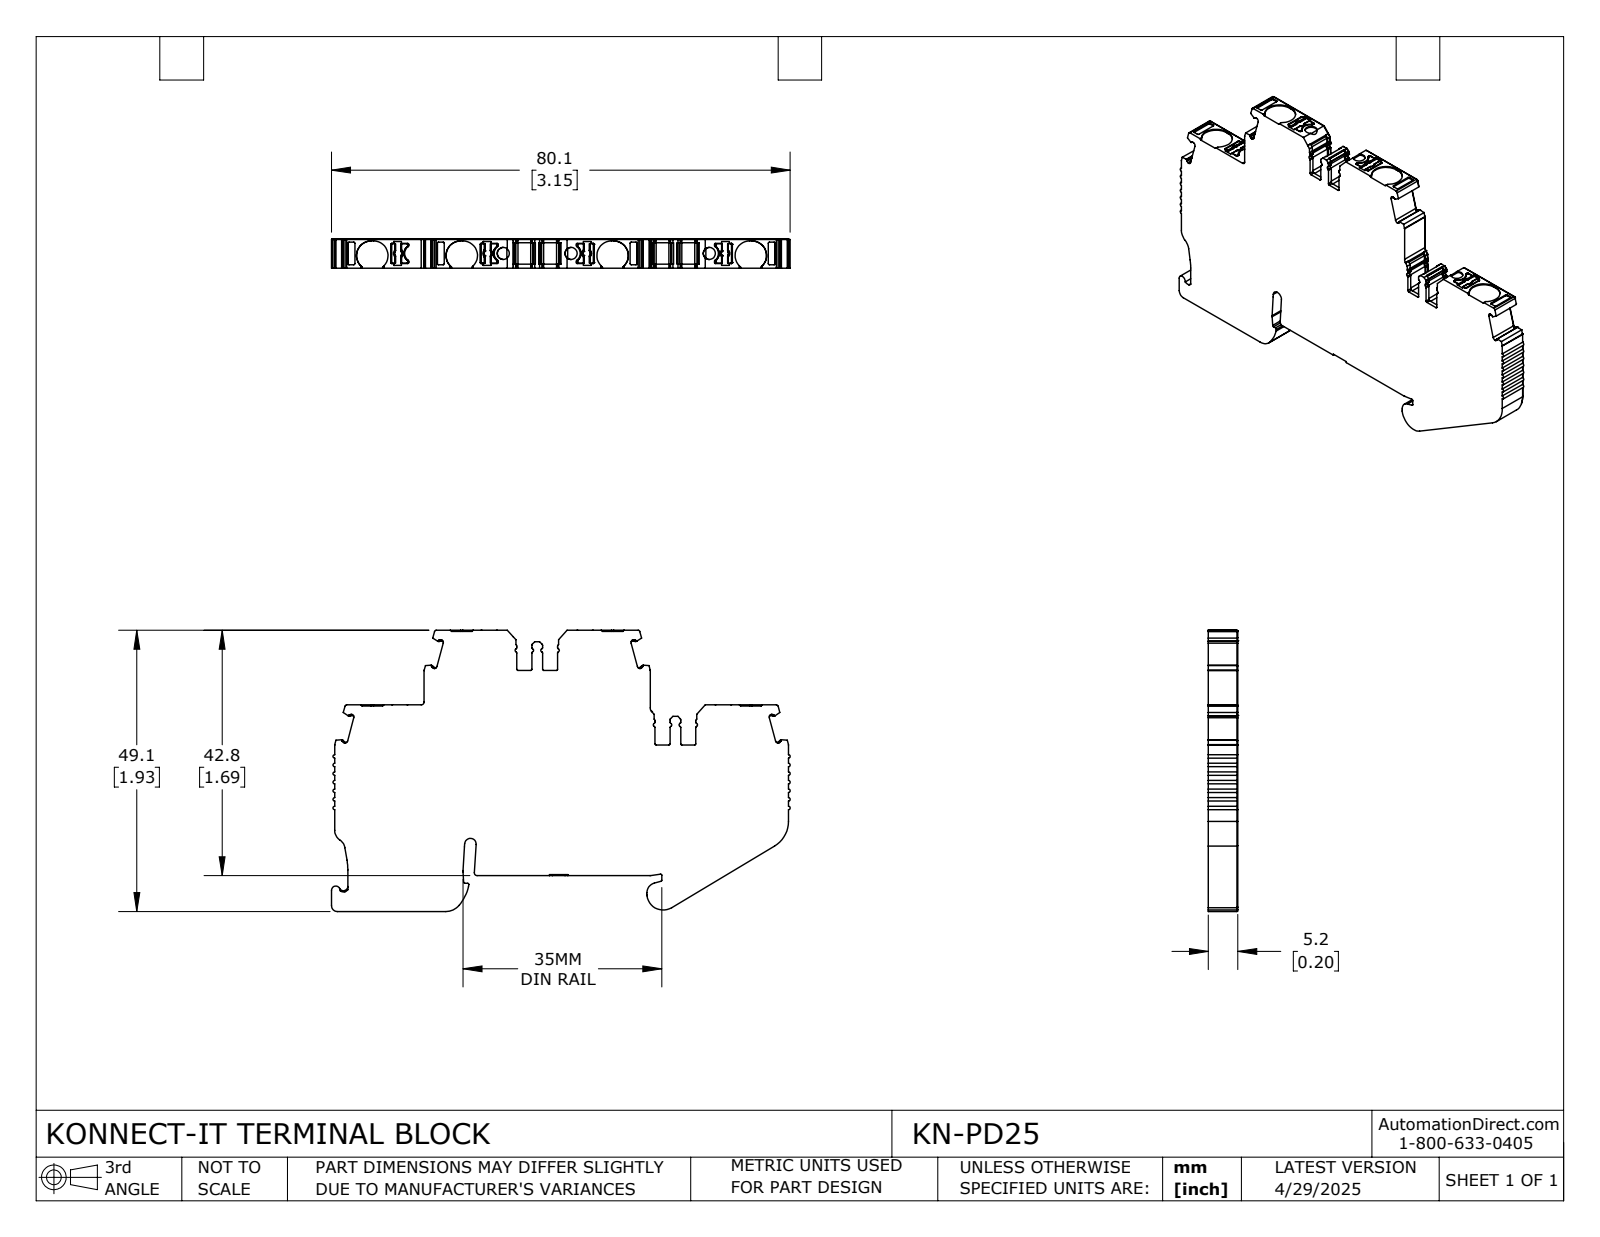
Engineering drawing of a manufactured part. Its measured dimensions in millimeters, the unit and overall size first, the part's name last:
Units: millimetres
Overall size (bounding box): 80.1 × 49.1 × 5.2
Round holes (diameter × count): ⌀2.1 ×3
Partial cylindrical surfaces — rounded edges, fillets, slot ends (radius × count): R0.2 ×100, R0.3 ×57, R0.1 ×41, R0.5 ×21, R0.4 ×17, R0.2 ×16, R0.6 ×9, R0.2 ×8
Main face-to-face distances: 5.2, 13, 6.2, 42.6, 29.6, 48.9, 2, 35.9, 12.8, 24.1
Hole centre spacings: 11.8, 24.1, 36
Volume: 14 600 mm³ · Surface area: 7 503 mm²
Bodies: 1 solid, 979 faces (470 planar, 438 cylindrical, 71 other)
Part name (STEP PRODUCT): KN-PD25
STEP written by: SolidWorks 2024 (CONFIG_CONTROL_DESIGN)
